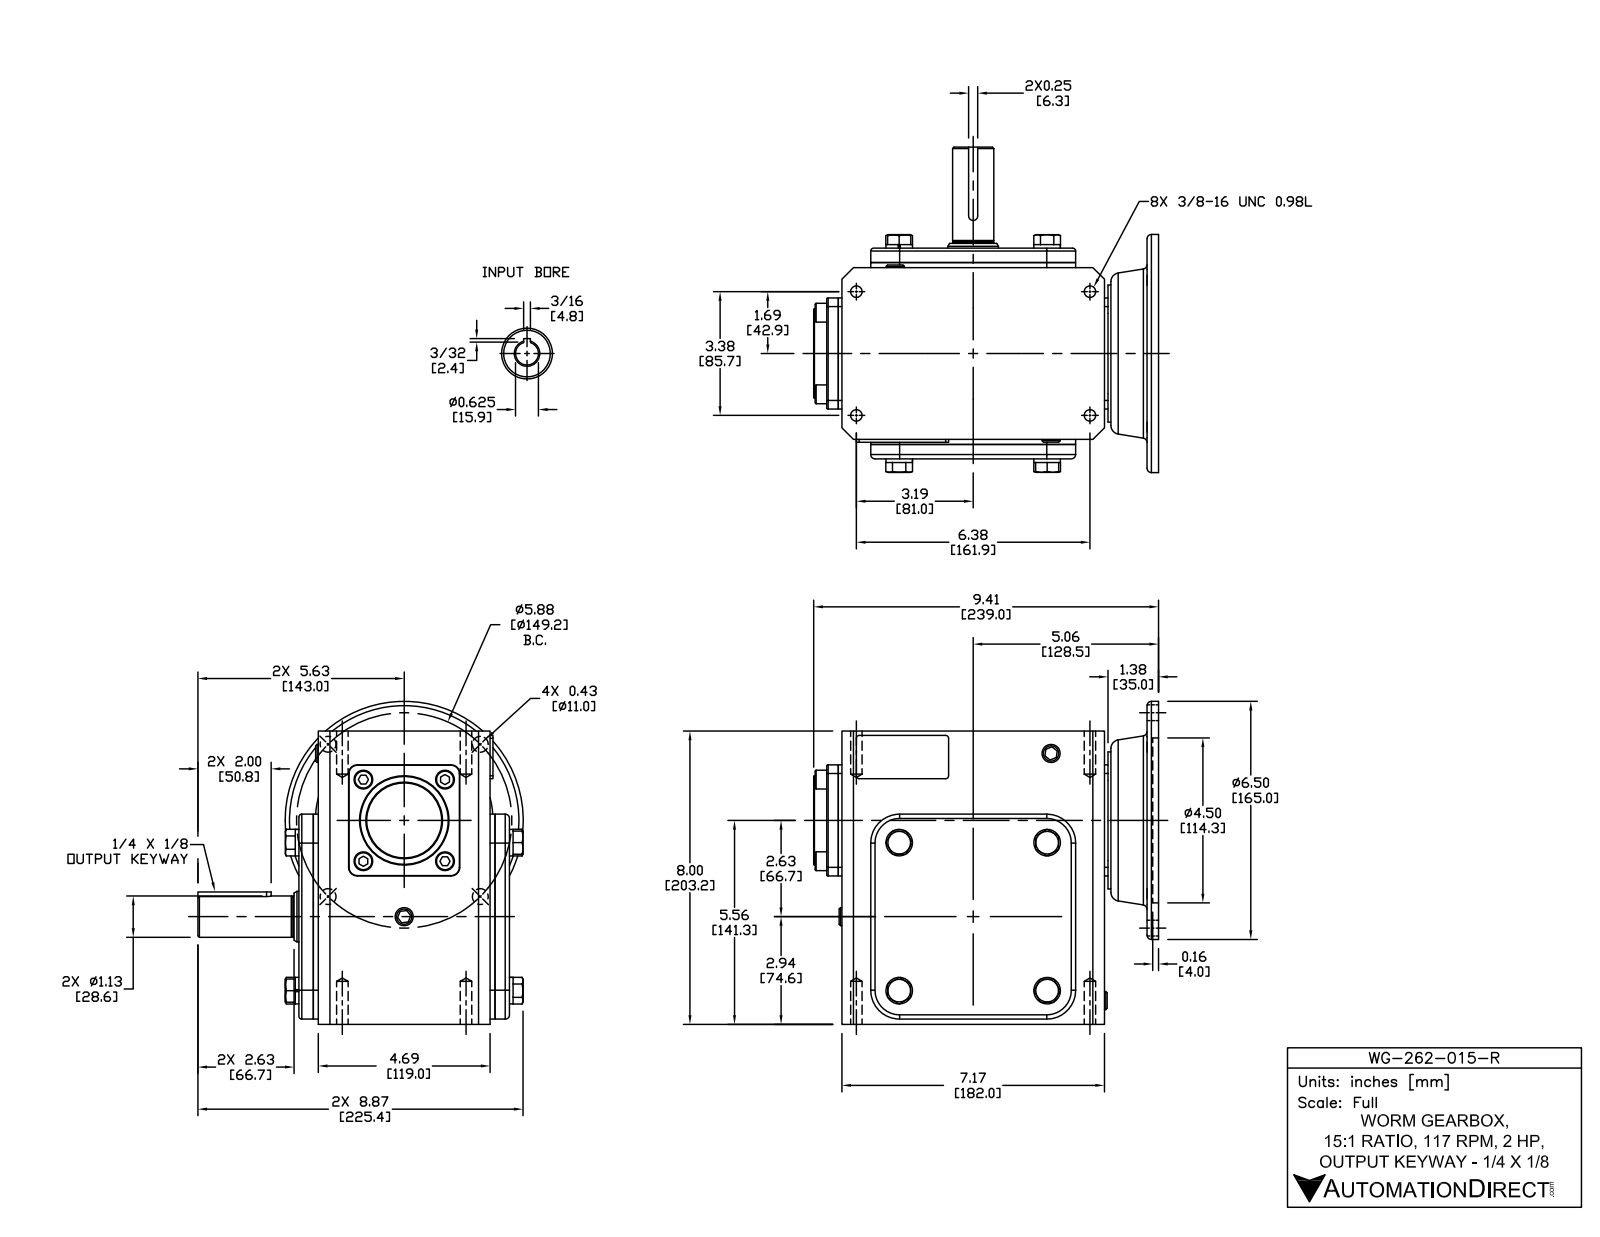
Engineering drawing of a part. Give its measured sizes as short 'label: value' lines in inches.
name: WG-262-015-R
written by: SolidWorks 2015 (CONFIG_CONTROL_DESIGN)
unit: in
bodies: 37 solids, 527 faces (293 planar, 138 cylindrical, 96 other)
size: 9.409 × 8.878 × 8.811
volume: 318.1 in³; area: 613.7 in²
holes: 4× ⌀0.313, 4× ⌀0.406, 1× ⌀0.591, 1× ⌀0.625, 1× ⌀1.181, 1× ⌀1.378, 1× ⌀1.457, 1× ⌀1.969, 1× ⌀3.819, 1× ⌀4.5
bosses: 4× ⌀0.724, 4× ⌀0.512, 1× ⌀6.496, 1× ⌀2.441, 1× ⌀2.047, 1× ⌀1.142, 1× ⌀1.125, 1× ⌀1.113
rounds: 12× R0.079, 4× R0.118, 4× R0.236, 4× R0.787, 2× R0.02, 2× R0.039, 1× R0.125
face distances: 0.394, 4.961, 5.354, 5.217, 0.531, 0.138, 4.823, 8, 0.098, 7.264
hole spacings: 2.937, 4.154, 2.148, 3.375, 5.14, 5.875, 6.375, 7.213
